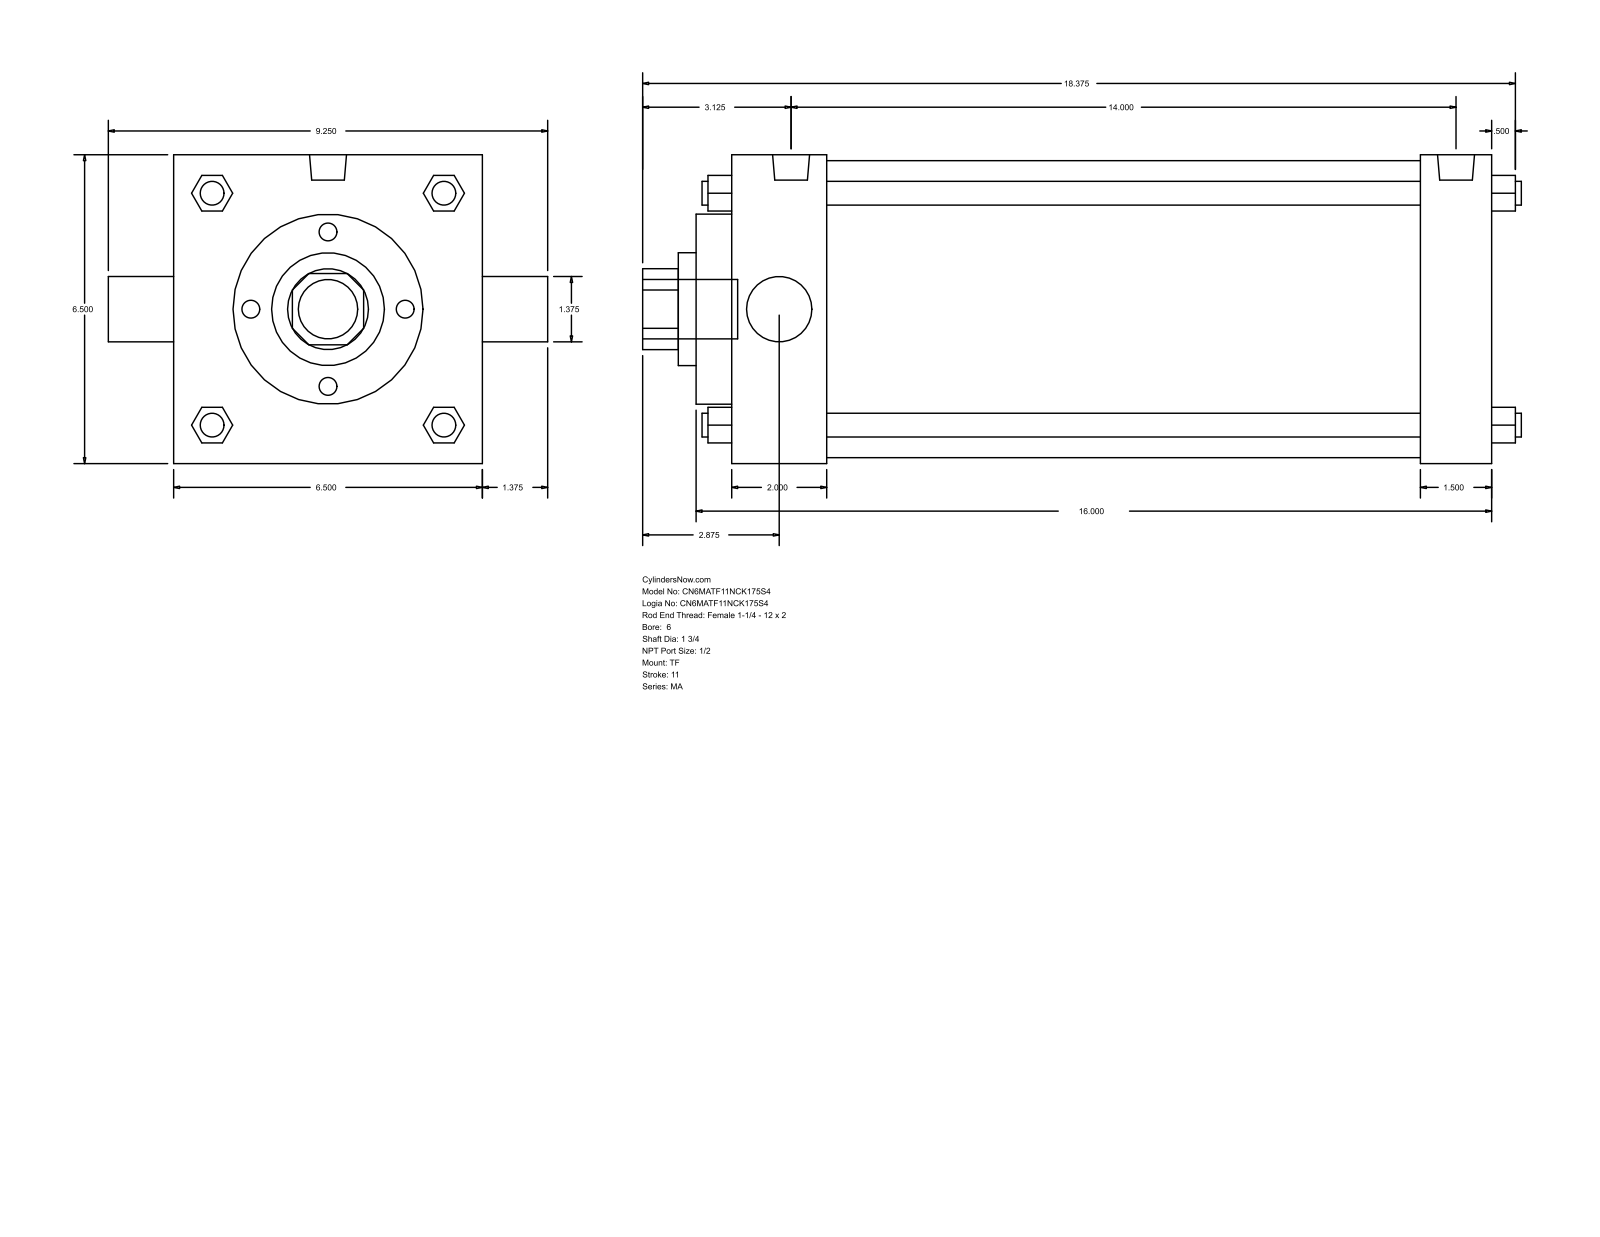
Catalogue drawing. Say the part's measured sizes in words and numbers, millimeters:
The part is named "MA_TF__0600_1.75". Its 3-D file was written by "GSSL Pune (CONFIG_CONTROL_DESIGN)". It is 0 solids with 122 faces: 93 planar, 29 cylindrical and 0 other. Overall it measures 469.9 by 234.95 by 165.1 millimeters. Round holes: 1 of diameter 34.92, 1 of diameter 44.45, 1 of diameter 60.33, 1 of diameter 101.6, 1 of diameter 158.75. Round bosses or shafts: 4 of diameter 12.7, 3 of diameter 17.46, 2 of diameter 19.77, 1 of diameter 31.75. Partial cylindrical surfaces (rounded edges, fillets, slot ends): 1 of radius 21.63. The main face-to-face distances are 165.1, 406.4, 19.05, 50.8, 368.31, 355.6, 317.51, 38.09, 69.85, 387.36.
